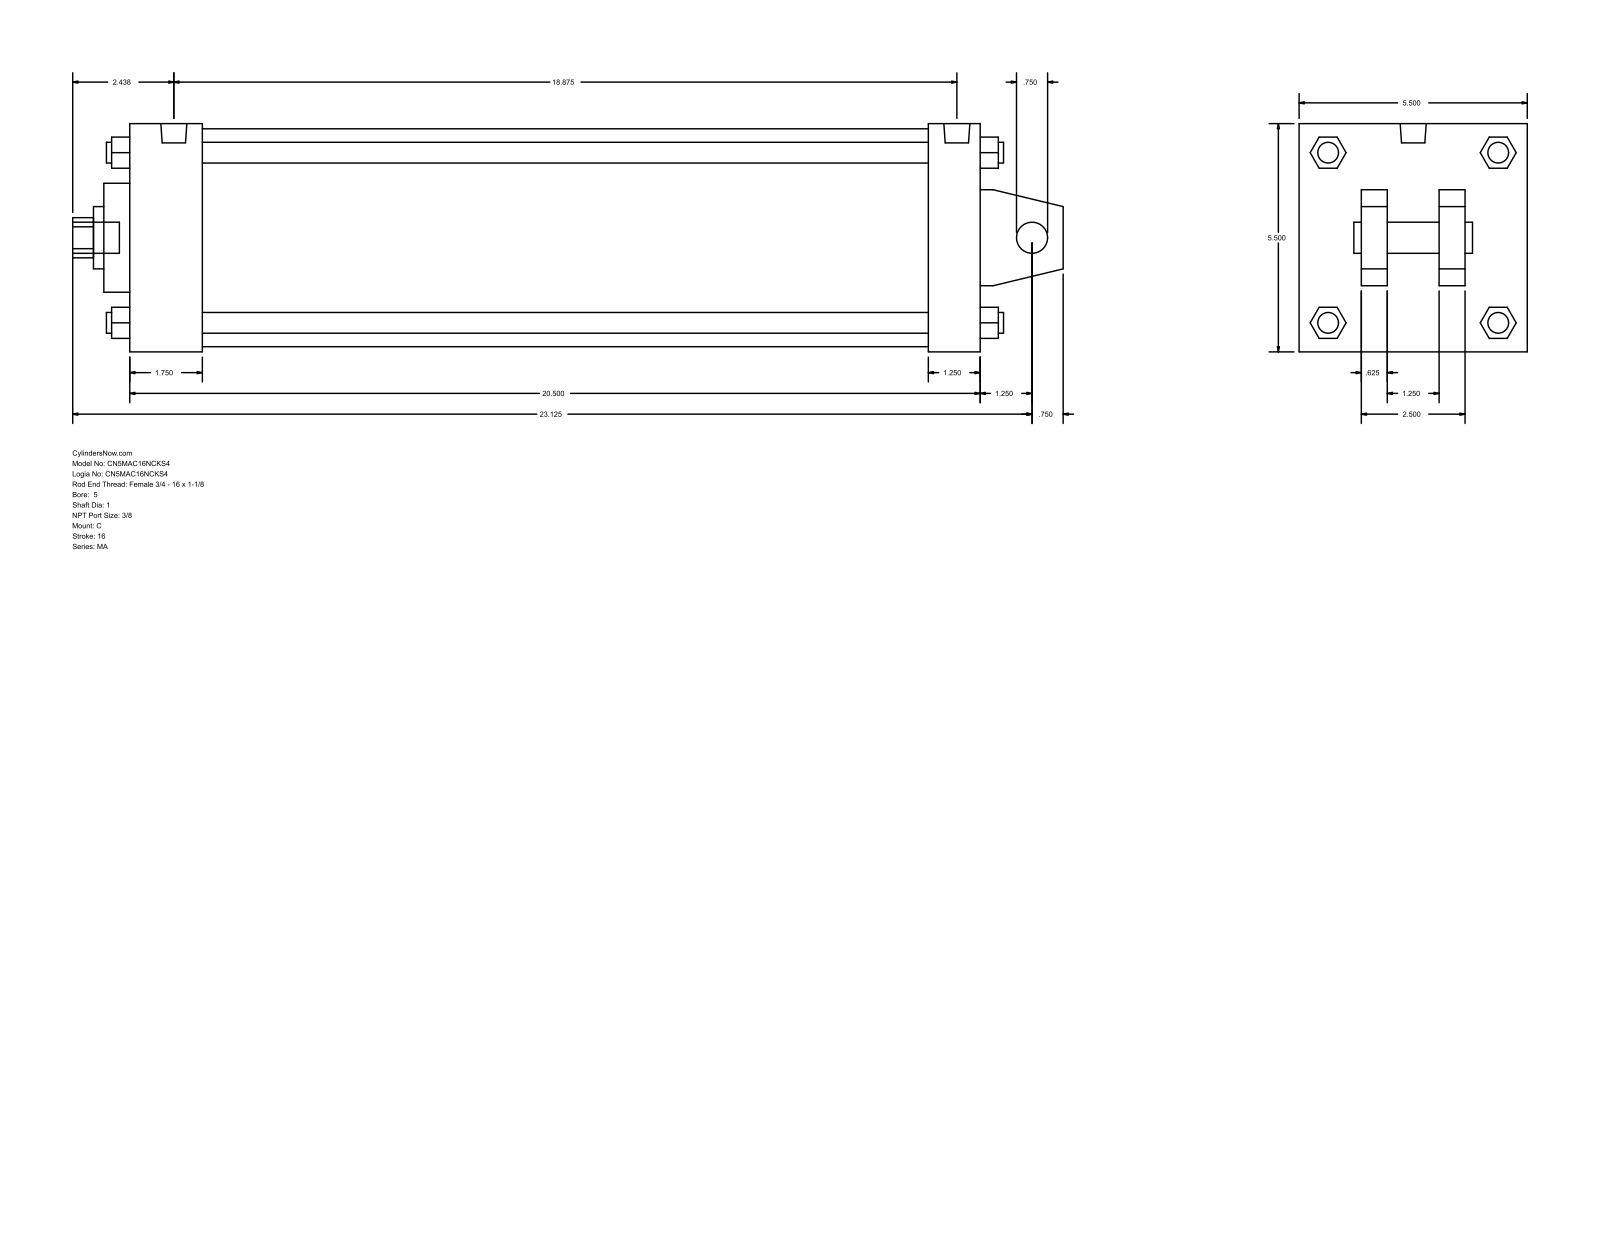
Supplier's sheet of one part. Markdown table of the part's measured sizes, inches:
| quantity | value |
| --- | --- |
| part name | MA_C__0500_1 |
| STEP written by | GSSL Pune (CONFIG_CONTROL_DESIGN) |
| units | inches |
| bodies | 0 solids, 141 faces (109 planar, 32 cylindrical, 0 other) |
| overall size | 23.875 × 5.5 × 5.5 |
| round holes (diameter × count) | 0.75 × 1, 1 × 1, 1.5 × 1, 2.625 × 1, 5.25 × 1 |
| round bosses / shafts (diameter × count) | 0.5 × 4, 0.437 × 4, 0.627 × 2, 0.75 × 1 |
| partial cylindrical surfaces (radius × count) | 0.484 × 1 |
| main face-to-face distances | 5.5, 20.5, 0.625, 19.25, 1.25, 1.75, 17.5, 18.75, 1.5, 4 |
